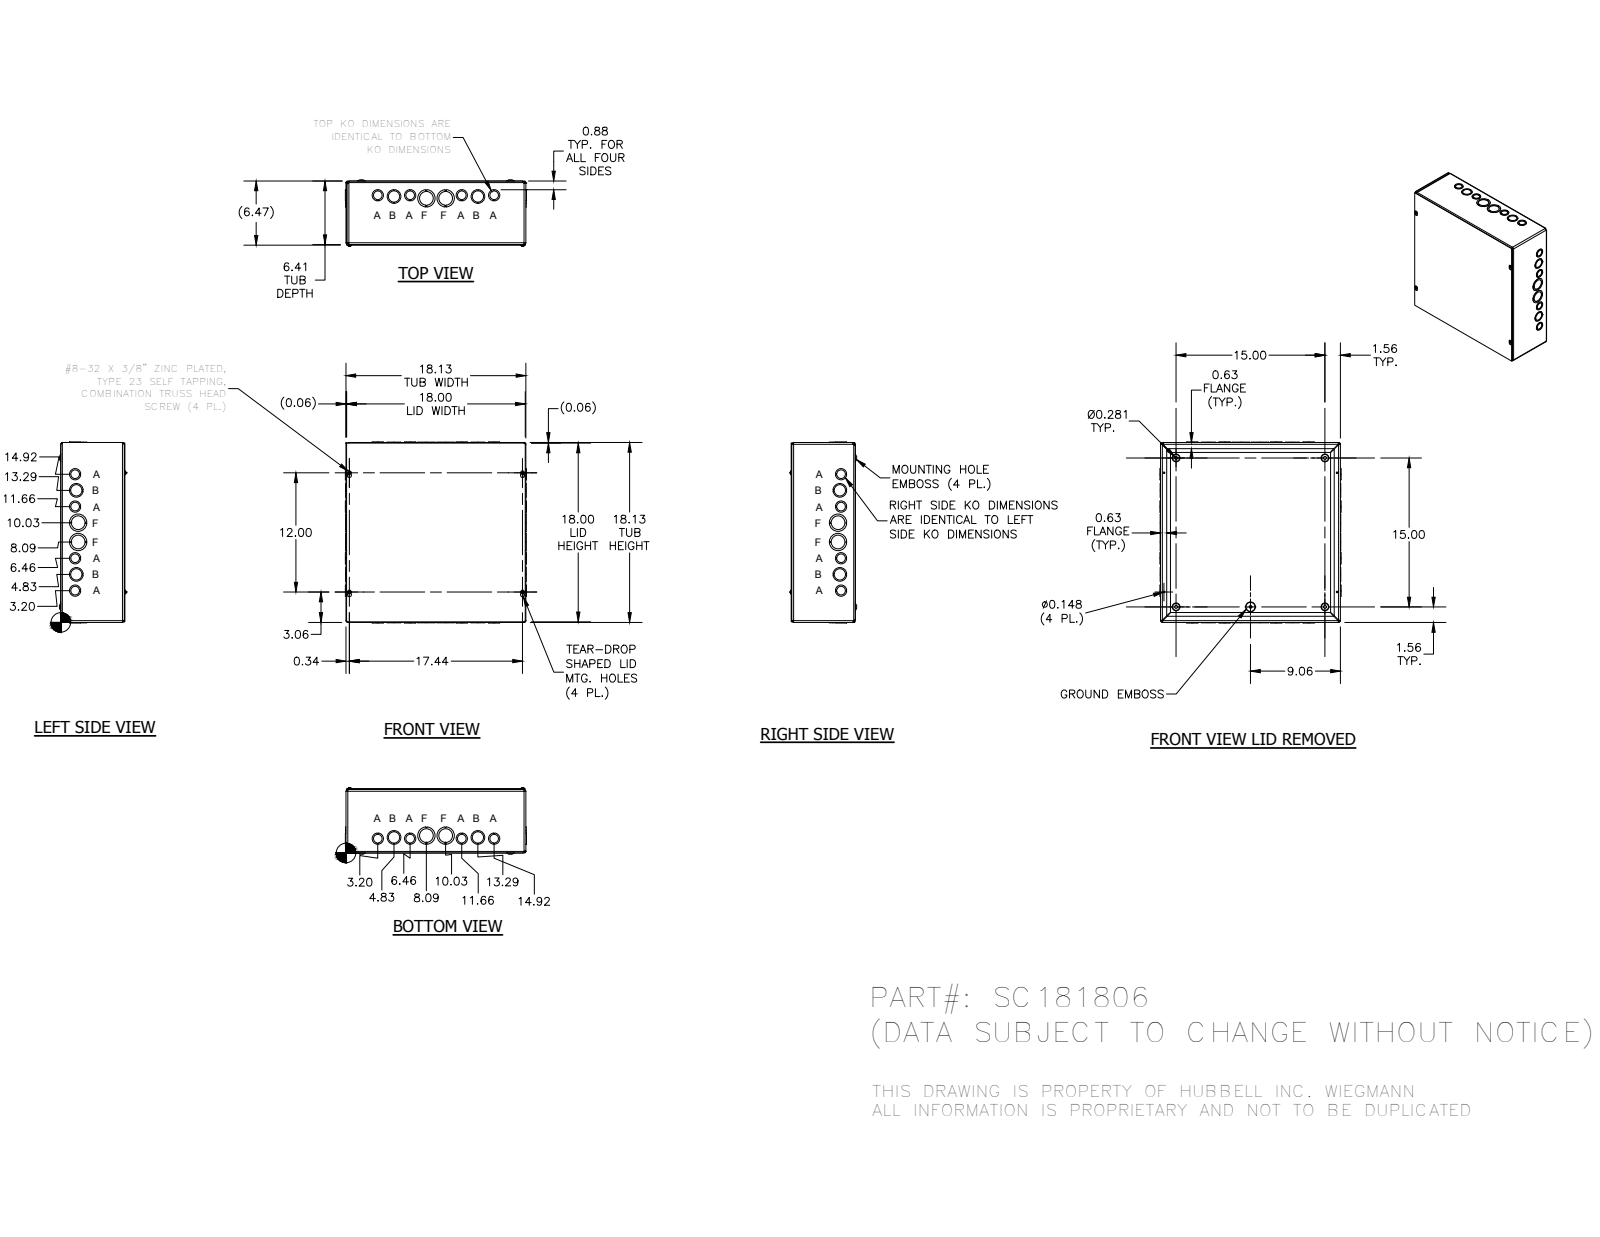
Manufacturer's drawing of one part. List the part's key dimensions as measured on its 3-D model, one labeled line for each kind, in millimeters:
Part name (STEP PRODUCT): SC1818BKP; SC181806WRA; SC1818LID; 34056 (+1 more)
STEP written by: Autodesk Inventor 2014 (AUTOMOTIVE_DESIGN)
Units: millimetres
Bodies: 38 solids, 1254 faces (837 planar, 259 cylindrical, 158 other)
Overall size (bounding box): 463.52 × 463.52 × 170
Round holes (diameter × count): ⌀28.57 ×12, ⌀22.22 ×8, ⌀34.92 ×8, ⌀3.76 ×4, ⌀7.62 ×4, ⌀44.45 ×4, ⌀4.19 ×1
Round bosses / shafts (diameter × count): ⌀9.75 ×4, ⌀4.17 ×4, ⌀5.8 ×1
Partial cylindrical surfaces — rounded edges, fillets, slot ends (radius × count): R3.17 ×12, R4.75 ×8, R1.4 ×4, R1.57 ×4, R2.38 ×4, R2.97 ×4, R3.15 ×4, R3.96 ×4
Main face-to-face distances: 1.57, 161.12, 162.69, 1.59, 162.71, 164.28, 1.58, 460.38, 458.8, 458.81
Hole centre spacings: 41.52, 42.15, 49.09, 82.94, 91.03, 132.17, 173.51, 214.88
